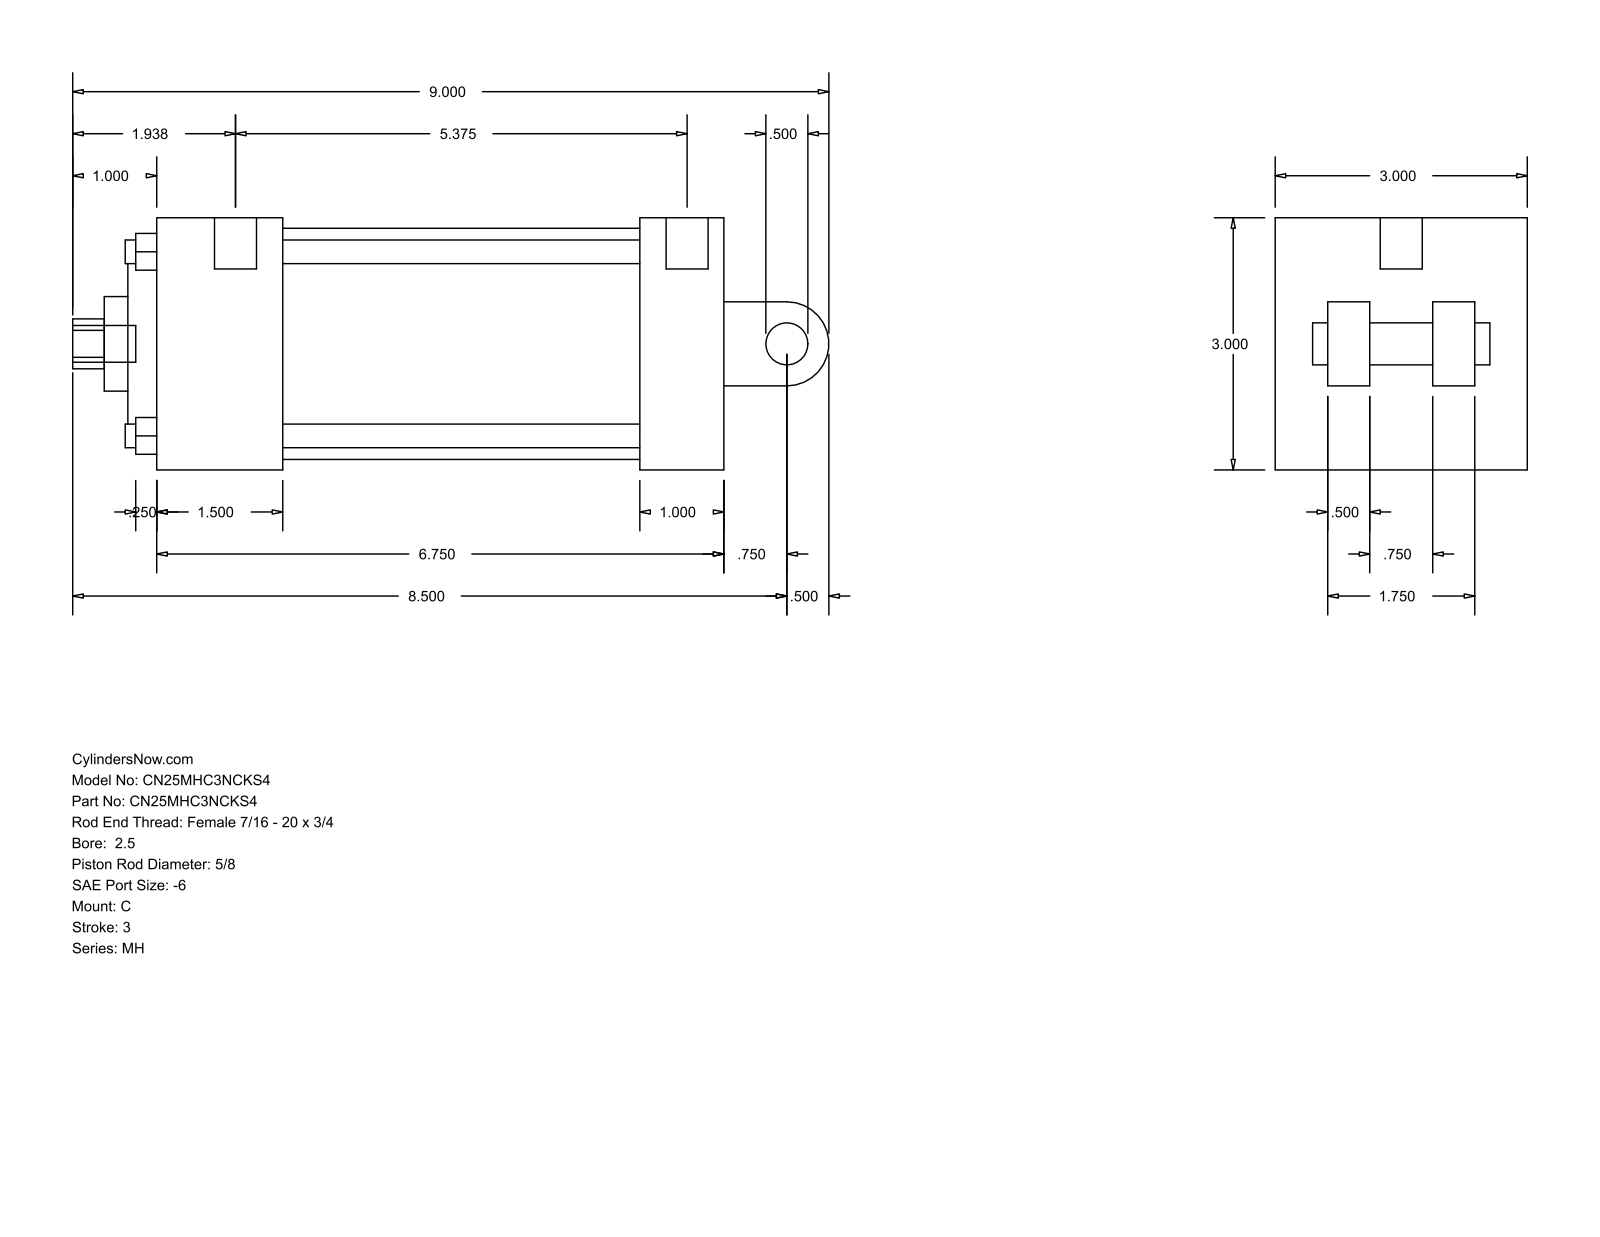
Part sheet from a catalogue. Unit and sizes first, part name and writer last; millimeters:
Units: millimetres
Overall size (bounding box): 228.6 × 76.2 × 76.2
Round holes (diameter × count): ⌀7.14 ×4, ⌀5.56 ×2, ⌀12.7 ×1, ⌀15.88 ×1, ⌀28.57 ×1, ⌀55.55 ×1, ⌀69.85 ×1
Round bosses / shafts (diameter × count): ⌀12.7 ×2, ⌀5.56 ×2, ⌀11.11 ×1
Partial cylindrical surfaces — rounded edges, fillets, slot ends (radius × count): R7.54 ×1, R12.7 ×1
Main face-to-face distances: 76.2, 25.4, 171.45, 15.87, 146.05, 38.1, 107.95, 133.35, 8.73, 46.83
Hole centre spacings: 39.33, 55.62, 78.66, 3.17
Bodies: 0 solids, 101 faces (71 planar, 30 cylindrical, 0 other)
Part name (STEP PRODUCT): MH_C__0250_0.625
STEP written by: GSSL Pune (CONFIG_CONTROL_DESIGN)
